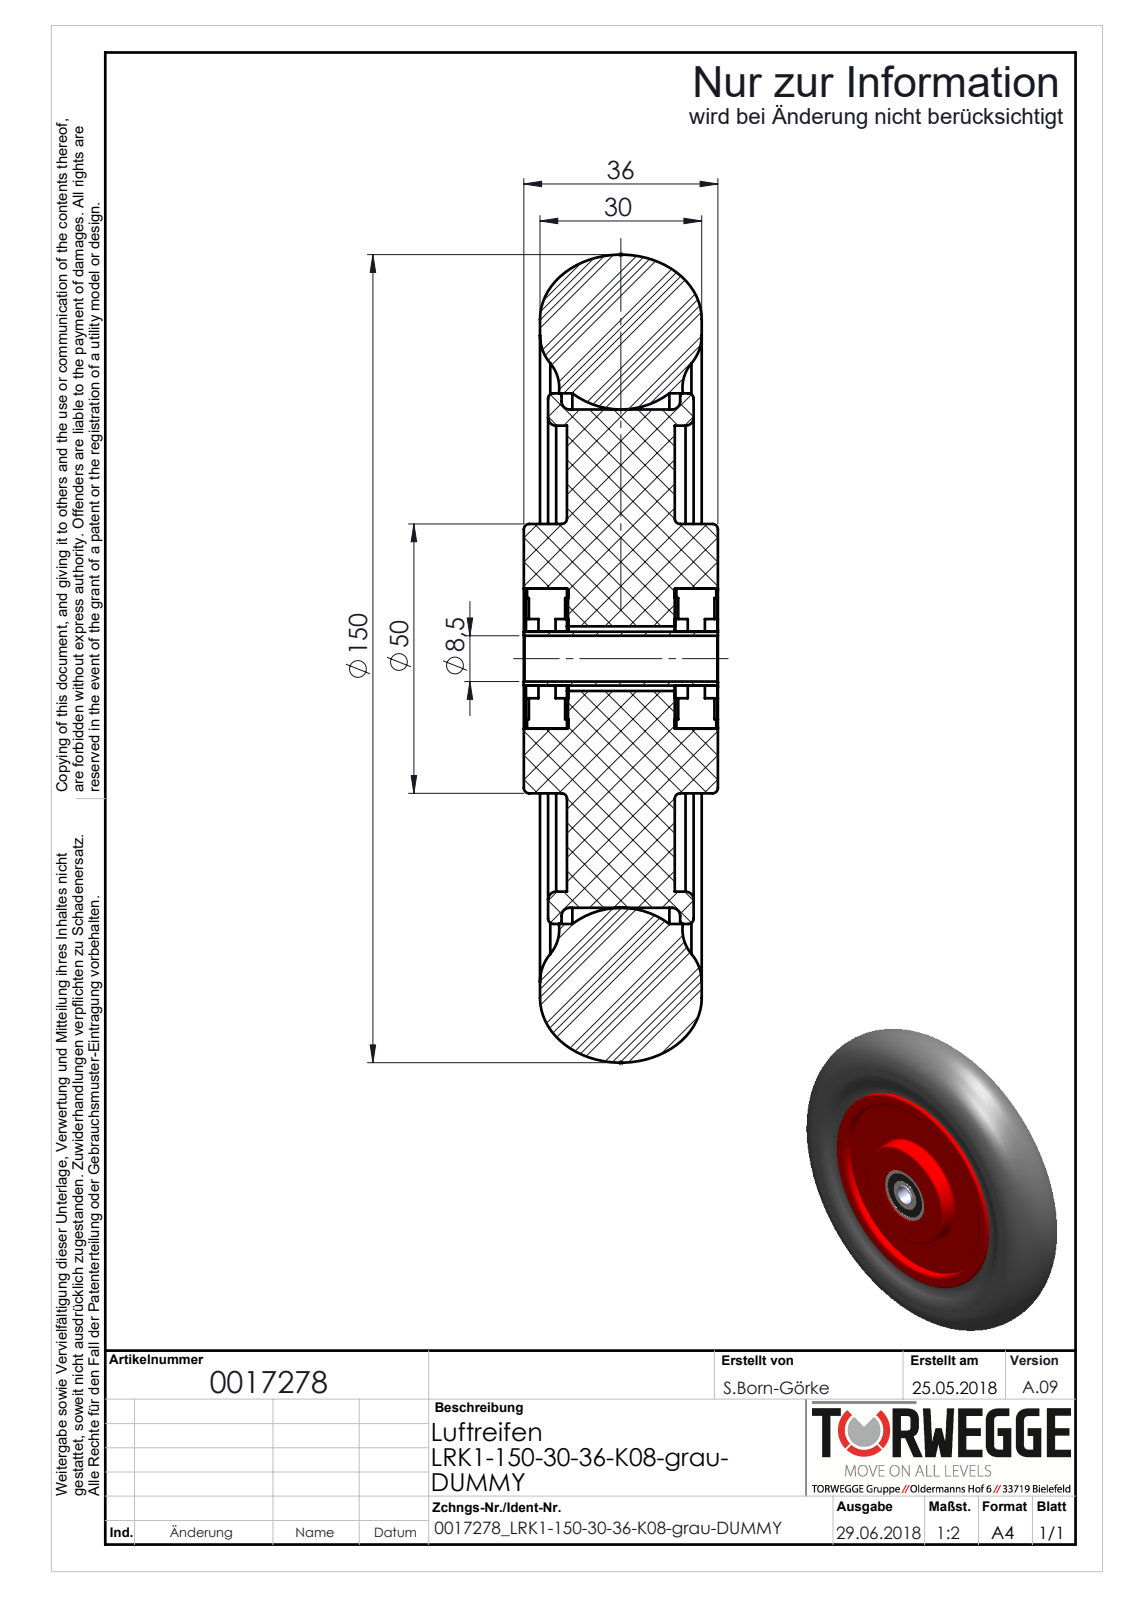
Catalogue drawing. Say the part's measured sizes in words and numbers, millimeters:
The part is named "SET_150x30_Decke_DUMMY; 0030880_DIN625-6000-10-2RS; 0017278_LRK1-150-30-36-K08-grau-DUMMY; Felge-FK-150-36-KS-rot_DUMMY (+1 more)". Its 3-D file was written by "SolidWorks 2018 (AUTOMOTIVE_DESIGN)". It is 3 solids with 140 faces: 26 planar, 52 cylindrical and 62 other. Overall it measures 150 by 150 by 36 millimeters. Its volume is 430 058 cubic millimeters and its surface area 72 688 square millimeters. Round holes: 1 of diameter 8.5, 1 of diameter 10, 1 of diameter 12, 1 of diameter 22.5, 1 of diameter 26, 1 of diameter 86.5, 1 of diameter 98.5. Round bosses or shafts: 1 of diameter 92.5, 1 of diameter 50, 1 of diameter 14.7. The main face-to-face distances are 20, 8, 28, 3, 33, 5, 25, 4.5, 31.5, 1.5.
